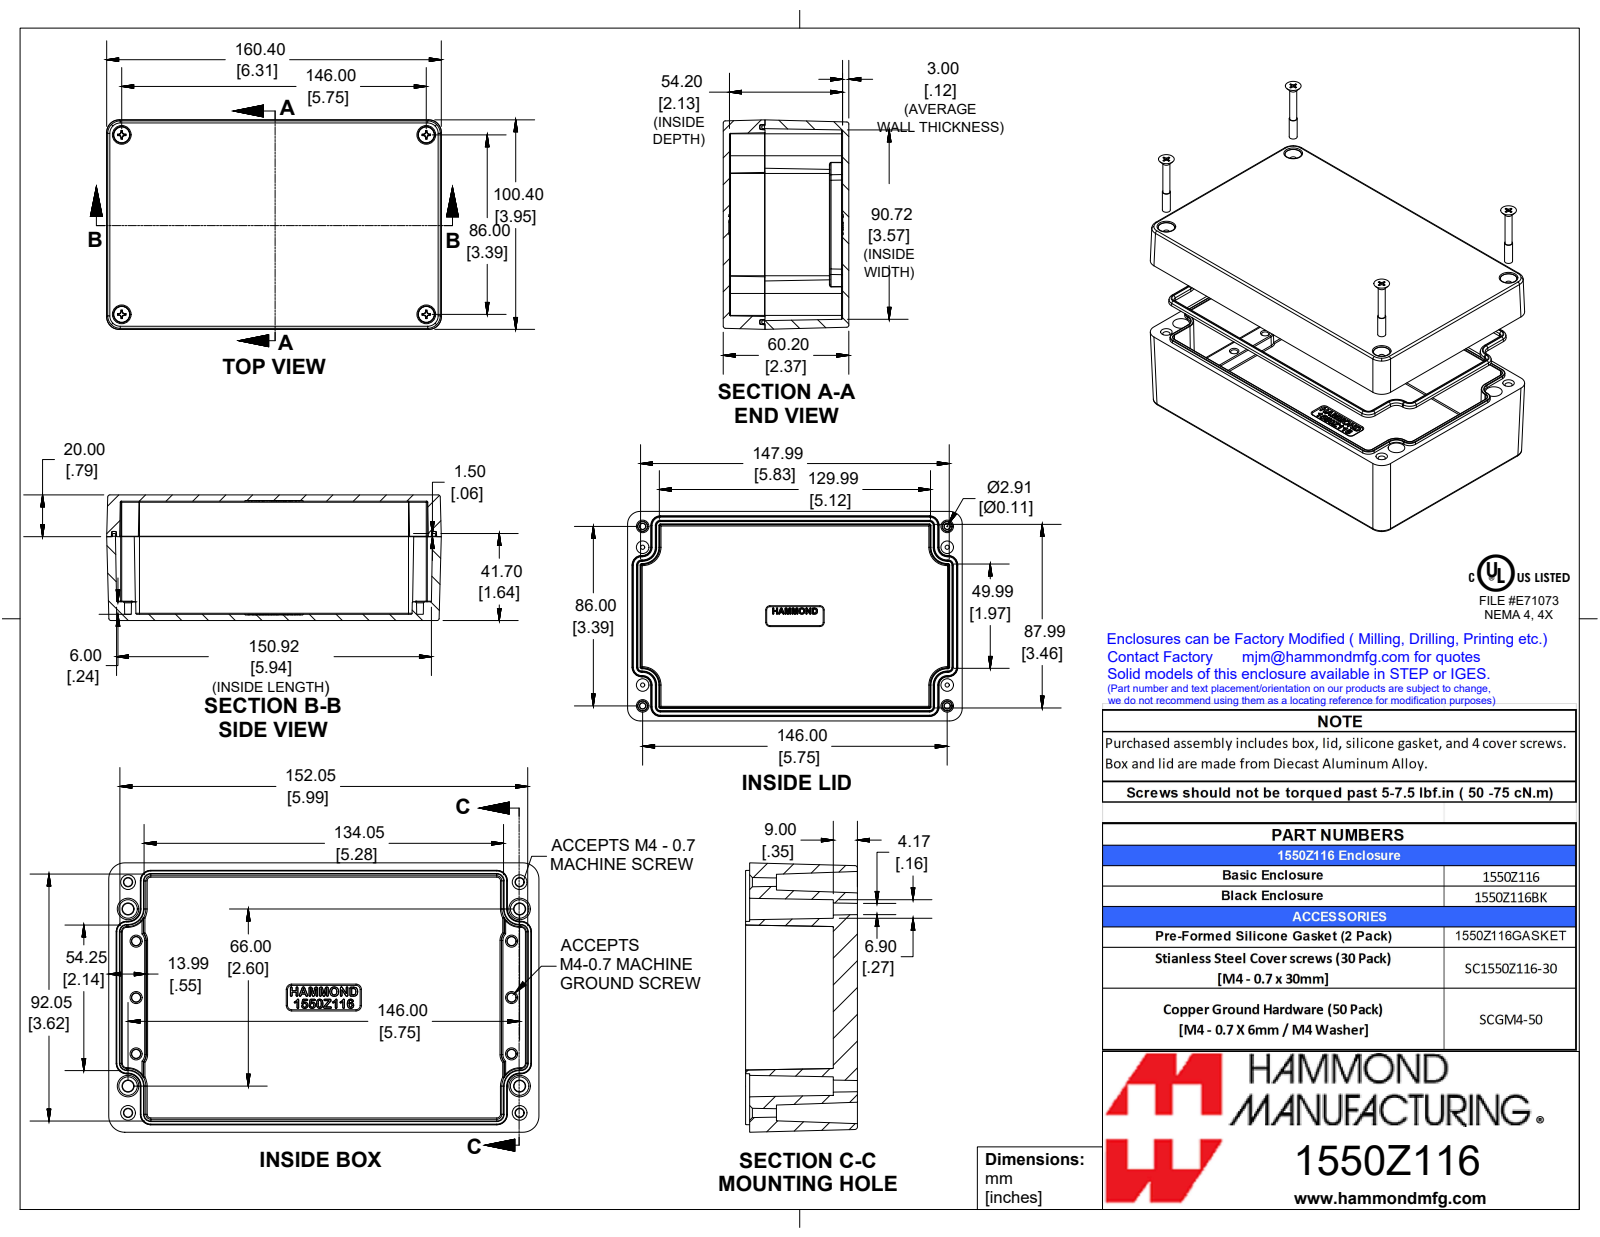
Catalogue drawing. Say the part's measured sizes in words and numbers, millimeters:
The part is named "1550Z116". Its 3-D file was written by "SolidWorks 2019 (AUTOMOTIVE_DESIGN)". It is 7 solids with 1299 faces: 360 planar, 240 cylindrical and 699 other. Overall it measures 160.4 by 100.4 by 60.2 millimeters. Its volume is 249 400 cubic millimeters and its surface area 135 100 square millimeters. Round bosses or shafts: 4 of diameter 7.6, 4 of diameter 3.9, 4 of diameter 3.3. Partial cylindrical surfaces (rounded edges, fillets, slot ends): 40 of radius 0.2, 28 of radius 0.5, 24 of radius 1, 20 of radius 0.3, 8 of radius 6, 4 of radius 4. The main face-to-face distances are 3, 57.2, 60.2, 54.2, 100.4, 90, 17, 20, 40.2, 37.2.
